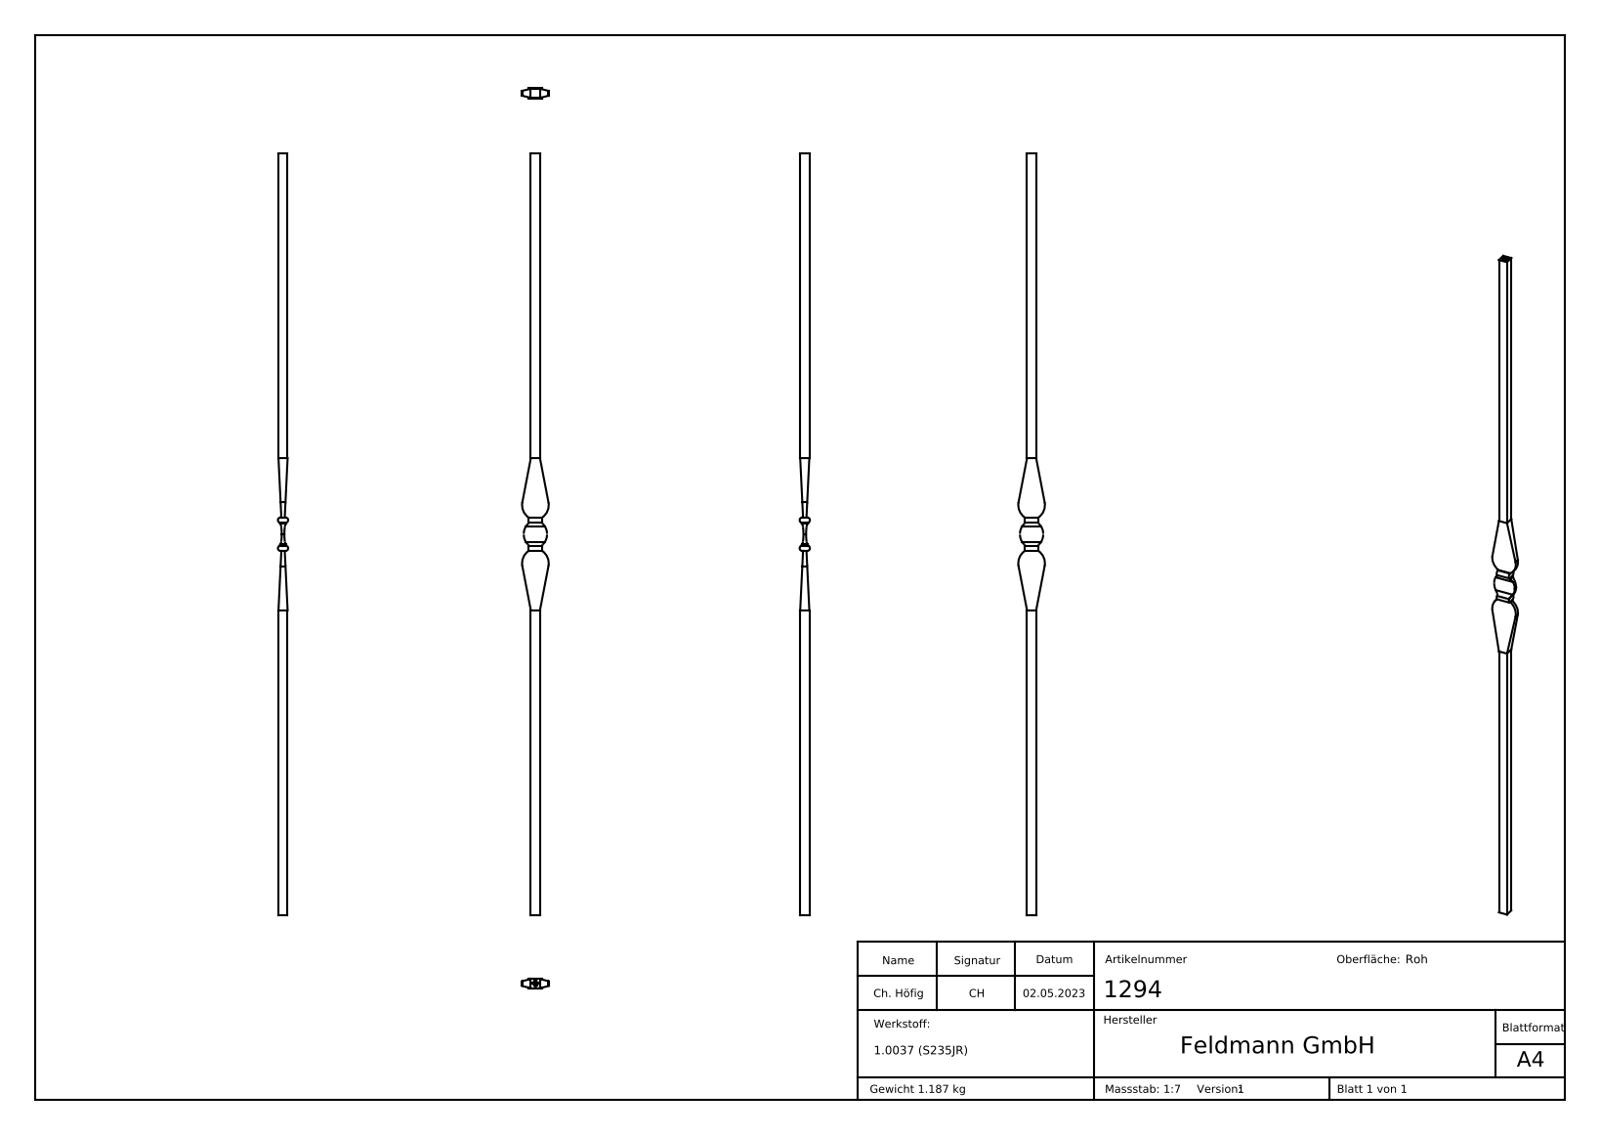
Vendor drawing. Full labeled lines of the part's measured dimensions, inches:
Part name (STEP PRODUCT): 1294
STEP written by: SolidWorks 2018 (CONFIG_CONTROL_DESIGN)
Units: inches
Bodies: 1 solid, 255 faces (150 planar, 22 cylindrical, 83 other)
Overall size (bounding box): 39.37 × 1.378 × 0.531
Volume: 9.289 in³ · Surface area: 81.02 in²
Partial cylindrical surfaces — rounded edges, fillets, slot ends (radius × count): R0.077 ×4, R0.138 ×4, R0.394 ×4, R0.709 ×4, R0.78 ×4, R2.982 ×2
Main face-to-face distances: 0.472, 0.094, 1.952, 0.118, 0.591, 0.709, 39.37, 18.819, 20.551, 1.732
